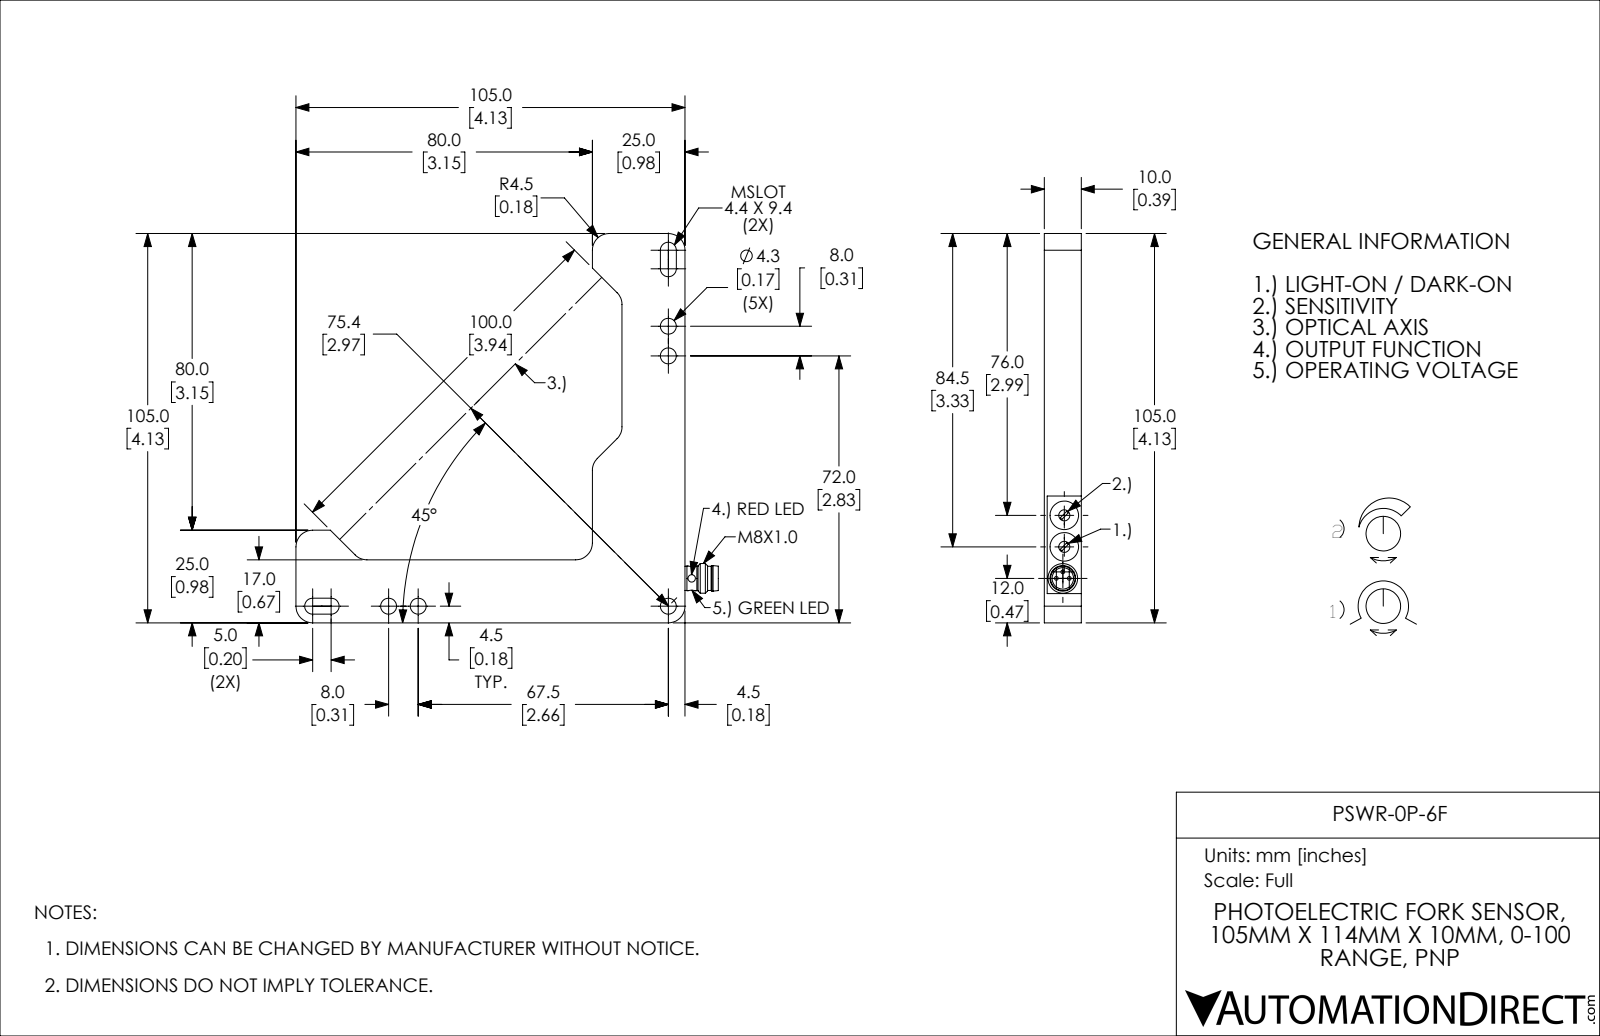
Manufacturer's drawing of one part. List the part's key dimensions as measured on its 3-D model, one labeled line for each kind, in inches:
Part name (STEP PRODUCT): PSWR-0P-6F
STEP written by: SolidWorks 2017 (AUTOMOTIVE_DESIGN)
Units: inches
Bodies: 1 solid, 90 faces (42 planar, 41 cylindrical, 7 other)
Overall size (bounding box): 4.488 × 4.134 × 0.394
Volume: 2.191 in³ · Surface area: 20.03 in²
Round holes (diameter × count): ⌀0.169 ×5, ⌀0.079 ×2, ⌀0.118 ×2, ⌀0.303 ×2, ⌀0.228 ×1
Round bosses / shafts (diameter × count): ⌀0.039 ×3, ⌀0.315 ×1, ⌀0.272 ×1, ⌀0.264 ×1, ⌀0.257 ×1
Partial cylindrical surfaces — rounded edges, fillets, slot ends (radius × count): R0.177 ×10, R0.085 ×4, R0.049 ×2
Main face-to-face distances: 0.394, 0.669, 4.134, 3.465, 0.984, 0.315, 3.15, 4.13, 0.98, 0.665
Hole centre spacings: 0.315, 2.657, 2.972, 3.987, 0.335, 0.335, 0.385, 0.669
